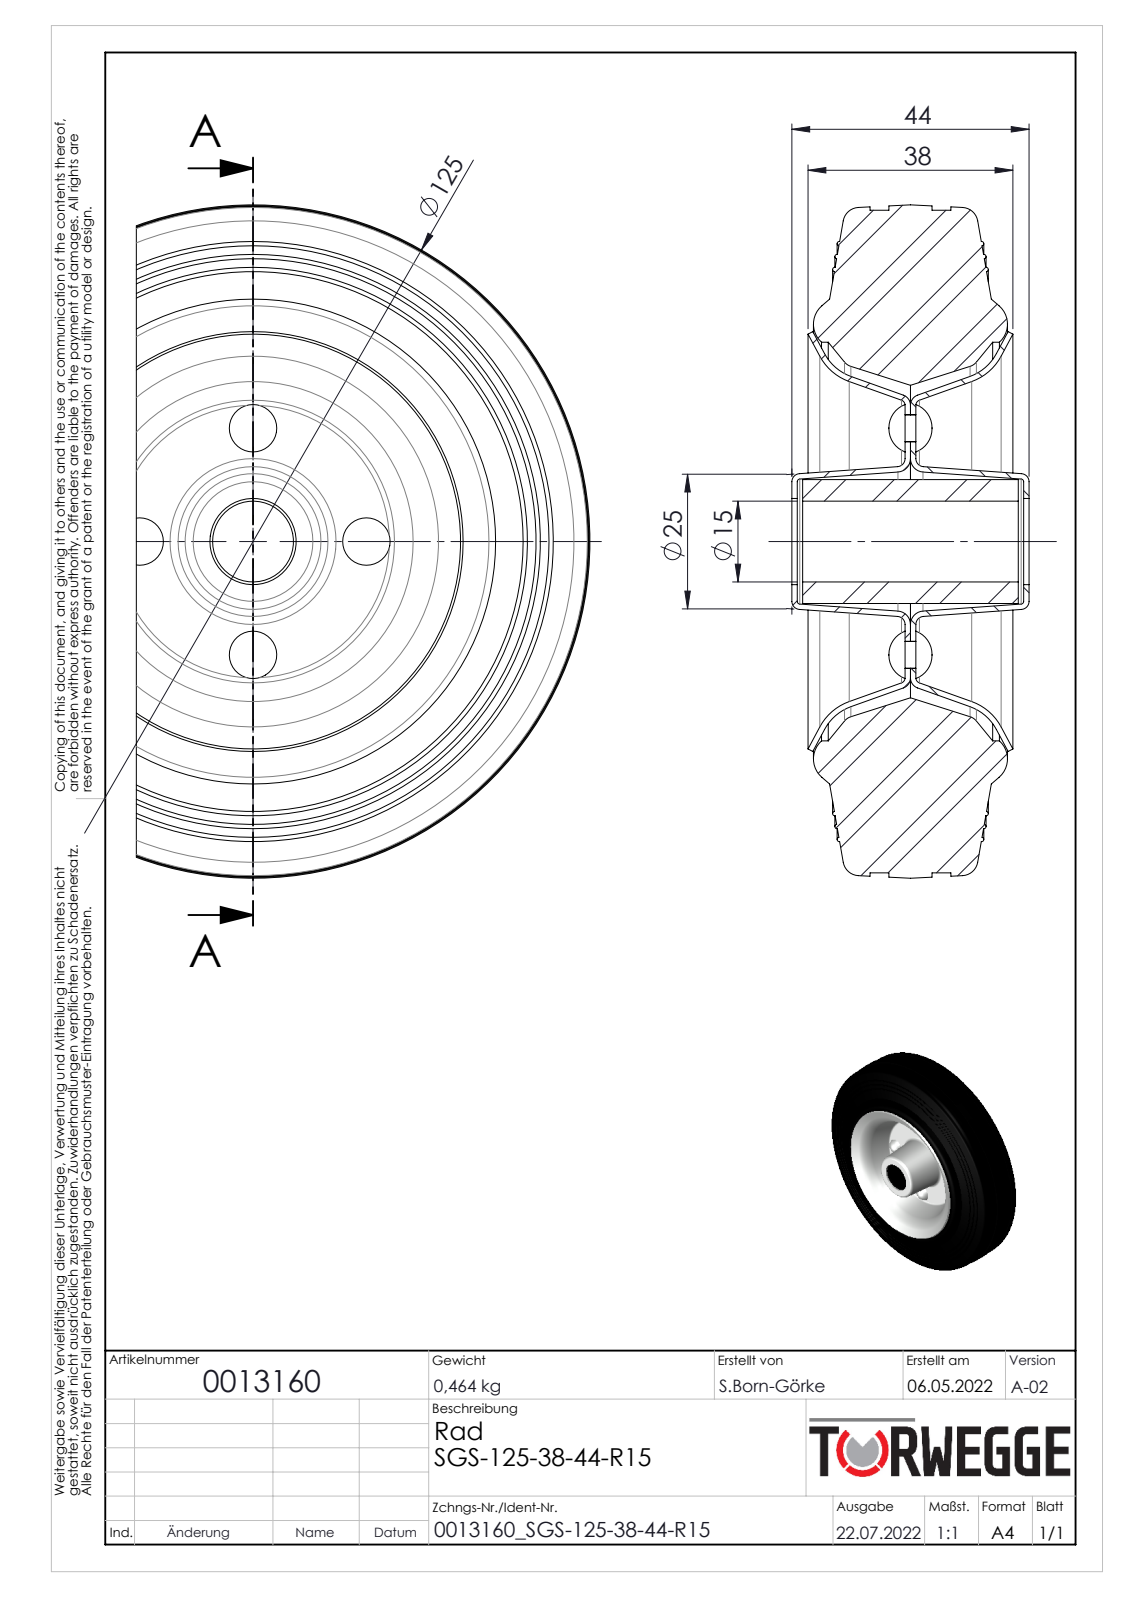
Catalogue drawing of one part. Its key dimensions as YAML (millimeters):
part_name: "0013160"
step_written_by: "SolidWorks 2020 (AUTOMOTIVE_DESIGN)"
units: millimeters
bodies: {solids: 8, faces: 198, planar: 22, cylindrical: 40, other: 136}
overall_size: [125, 125, 44]
volume: 284400
surface_area: 73546
round_holes:
  - {diameter: 5, count: 4}
  - {diameter: 15, count: 1}
  - {diameter: 16, count: 1}
  - {diameter: 74, count: 1}
round_bosses_or_shafts:
  - {diameter: 123, count: 1}
  - {diameter: 23, count: 1}
face_to_face_distances: [1, 2, 21, 20, 22, 3, 4, 5, 42, 3.5]
hole_center_spacings: [21.03, 29.74, 42.06]
